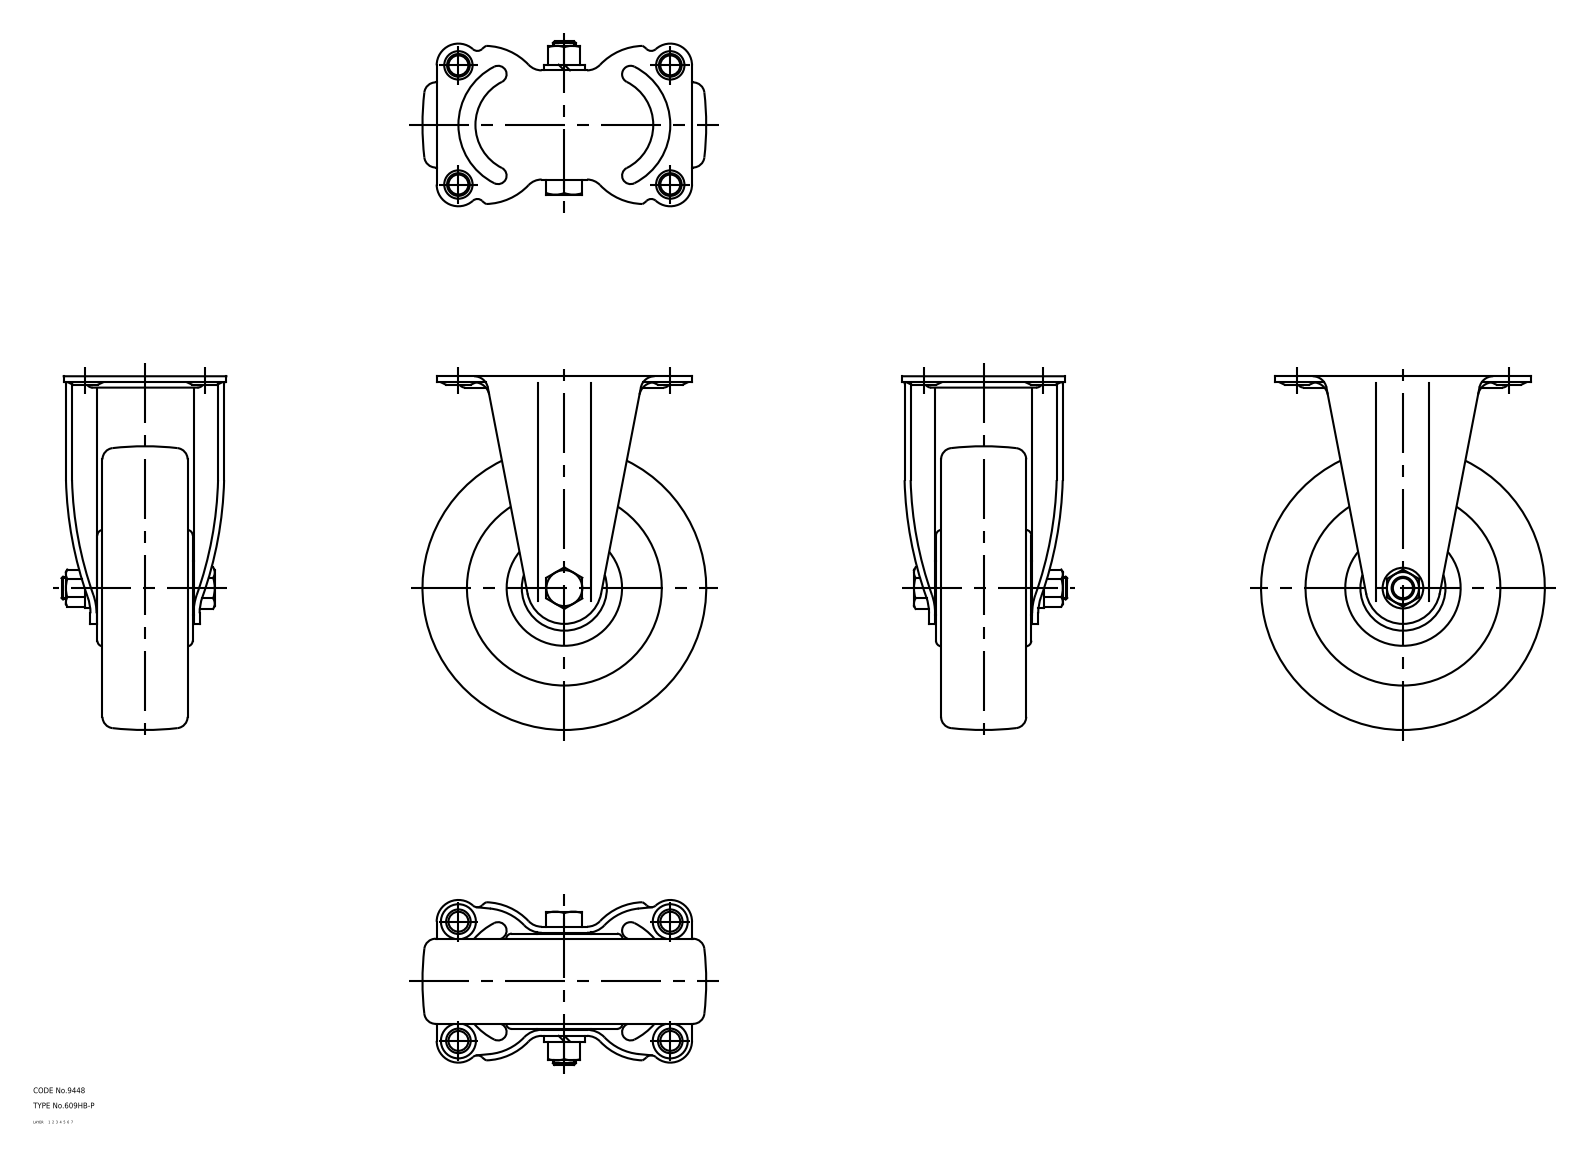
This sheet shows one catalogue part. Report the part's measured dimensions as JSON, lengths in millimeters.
{"part_name": "67124585; 67124598; 67124611", "step_written_by": "CADfix (AUTOMOTIVE_DESIGN)", "units": "millimeters", "bodies": {"solids": 3, "faces": 209, "planar": 0, "cylindrical": 0, "other": 209}, "overall_size": [187, 150, 87.15], "volume_mm3": 799696, "surface_area_mm2": 120481}
